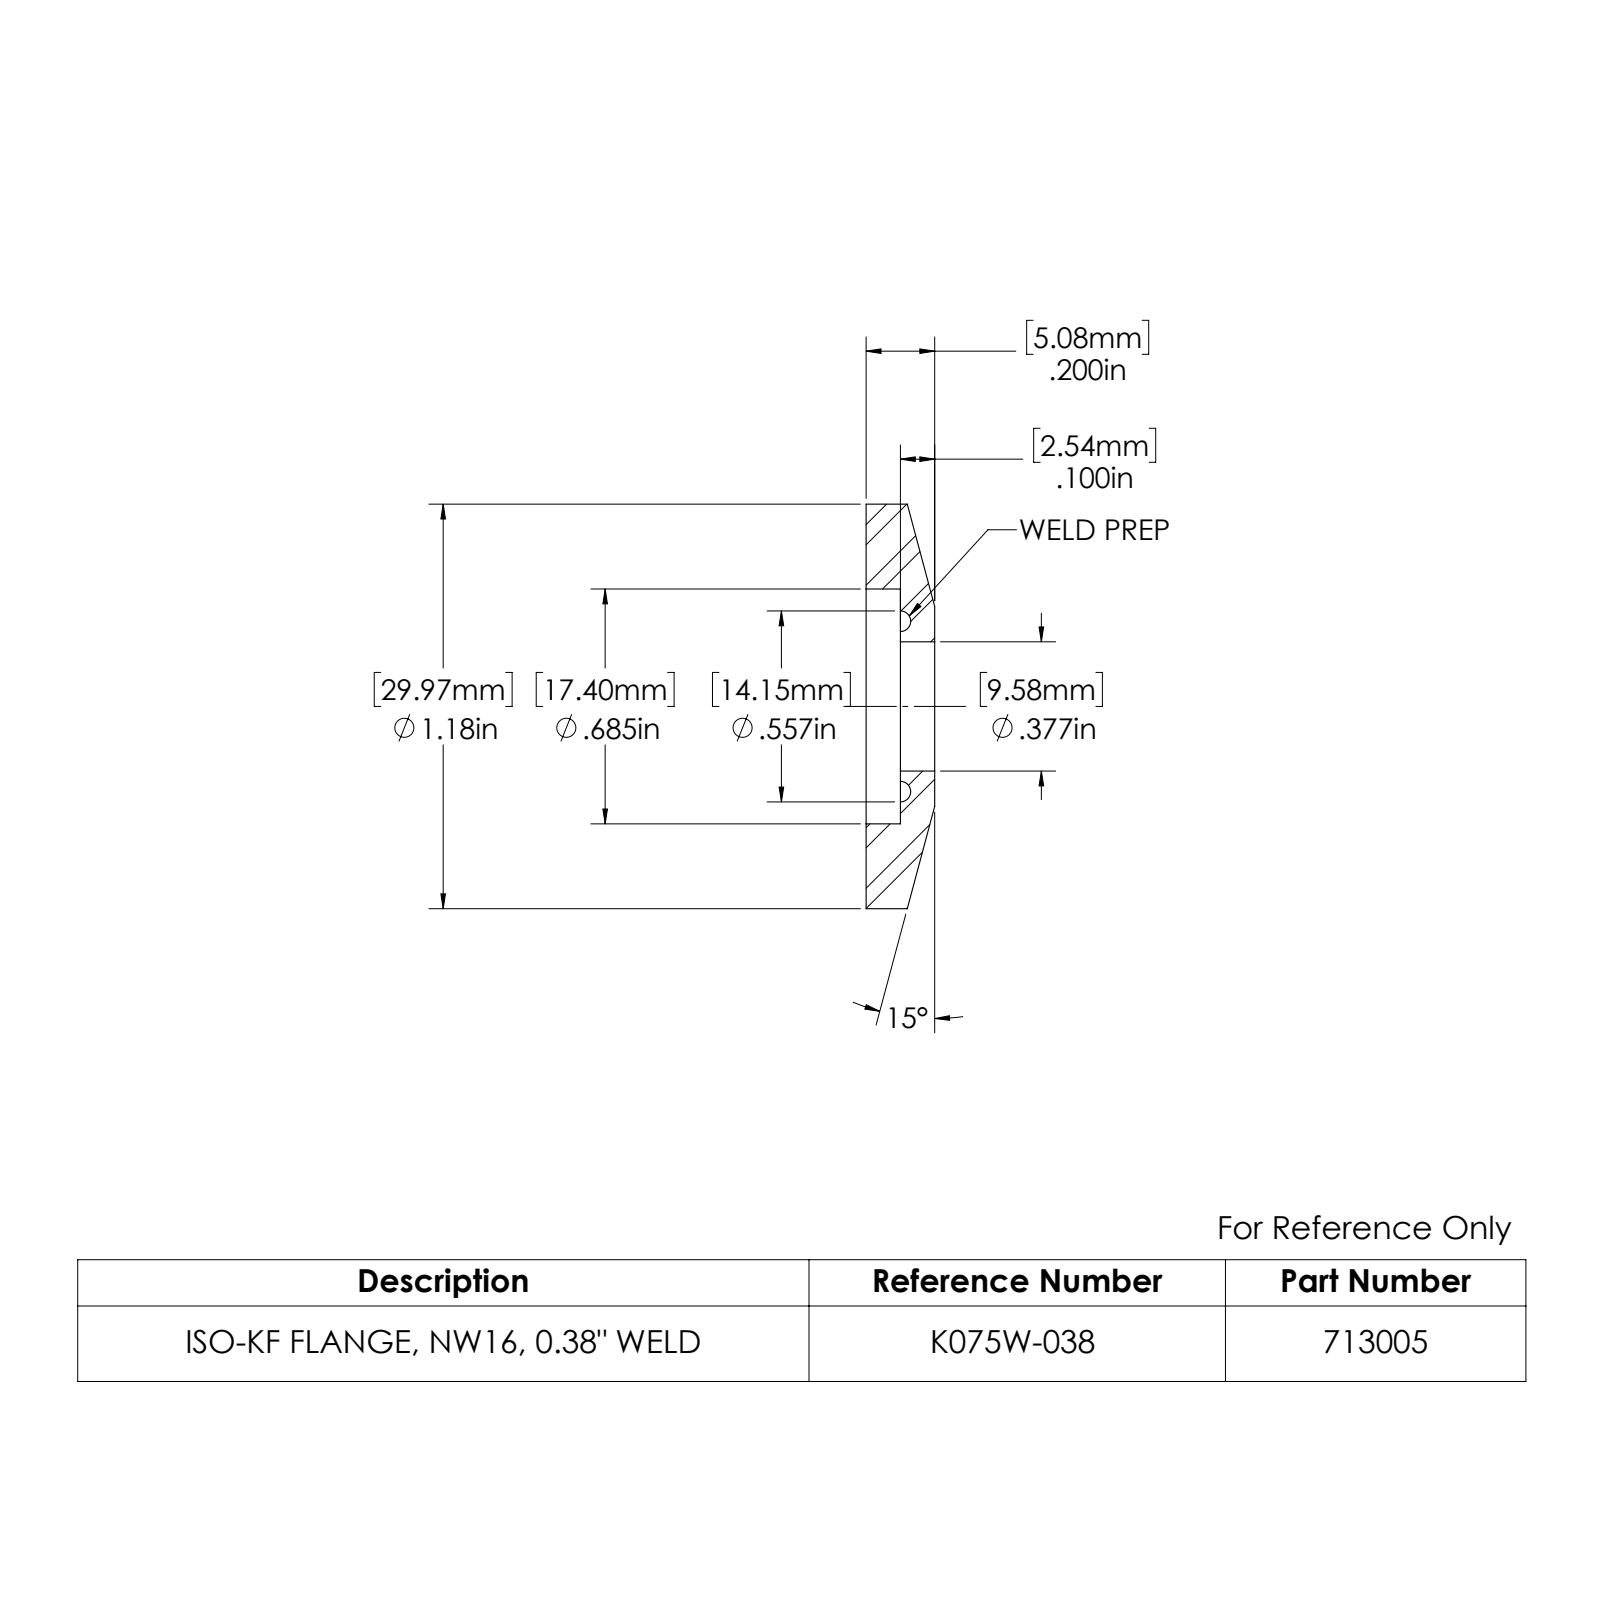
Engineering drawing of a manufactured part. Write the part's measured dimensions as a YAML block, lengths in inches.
part_name: "713005"
step_written_by: "SolidWorks 2022 (AUTOMOTIVE_DESIGN)"
units: inches
bodies: {solids: 1, faces: 14, planar: 4, cylindrical: 6, other: 4}
overall_size: [1.18, 1.18, 0.2]
volume: 0.132
surface_area: 2.825
round_holes:
  - {diameter: 0.377, count: 1}
  - {diameter: 0.685, count: 1}
round_bosses_or_shafts:
  - {diameter: 1.18, count: 1}
face_to_face_distances: [0.1, 0.2]
